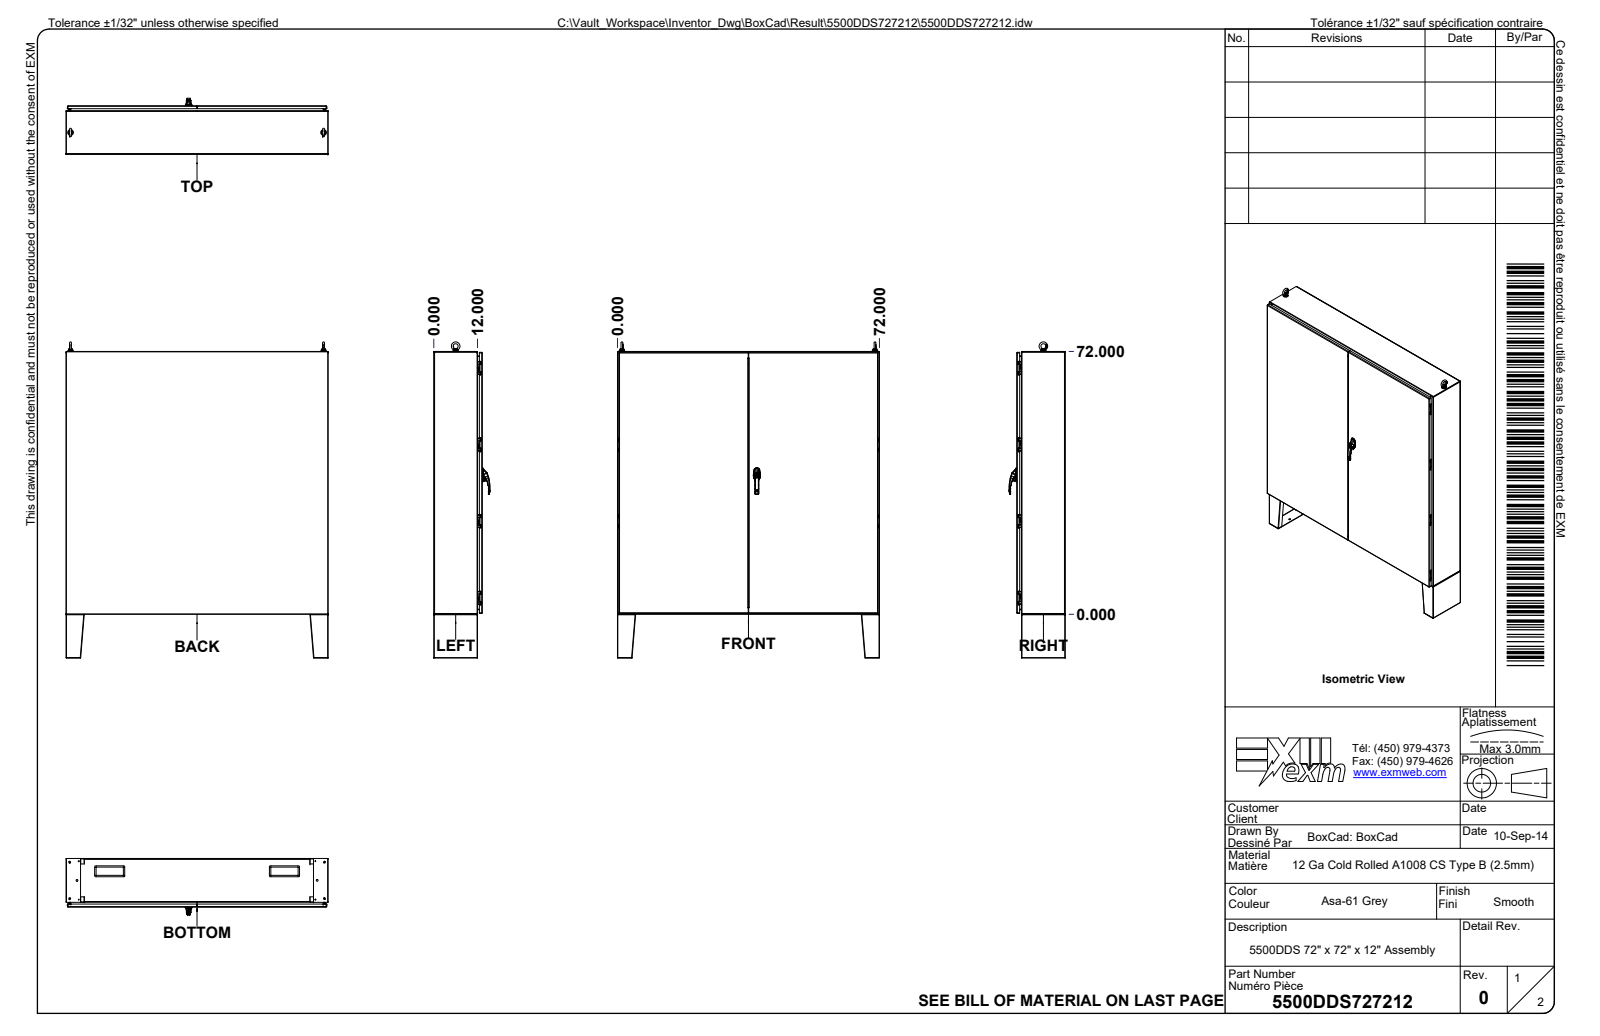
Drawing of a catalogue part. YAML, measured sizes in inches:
part_name: "5500DDS727212; 5500DDS727212B; 5500DDS727212B-P; 5500DDS727212LS-P (+8 more)"
step_written_by: "Autodesk Inventor 2024 (AUTOMOTIVE_DESIGN)"
units: inches
bodies: {solids: 275, faces: 36132, planar: 12457, cylindrical: 9061, other: 14614}
overall_size: [86.638, 72, 15.422]
volume: 2003
surface_area: 45738
round_holes:
  - {diameter: 0.177, count: 384}
  - {diameter: 0.03, count: 41}
  - {diameter: 0.201, count: 26}
  - {diameter: 0.043, count: 16}
  - {diameter: 0.167, count: 16}
  - {diameter: 0.315, count: 12}
  - {diameter: 0.394, count: 12}
  - {diameter: 0.5, count: 12}
  - {diameter: 0.512, count: 12}
  - {diameter: 0.625, count: 12}
  - {diameter: 0.203, count: 8}
  - {diameter: 0.341, count: 8}
round_bosses_or_shafts:
  - {diameter: 0.272, count: 264}
  - {diameter: 0.03, count: 41}
  - {diameter: 0.232, count: 34}
  - {diameter: 0.039, count: 30}
  - {diameter: 0.289, count: 20}
  - {diameter: 0.177, count: 20}
  - {diameter: 0.39, count: 15}
  - {diameter: 0.874, count: 8}
partial_cylinders:
  - {radius: 0.02, count: 636}
  - {radius: 0.039, count: 484}
  - {radius: 0.008, count: 285}
  - {radius: 0.012, count: 231}
  - {radius: 0.01, count: 215}
  - {radius: 0.031, count: 189}
  - {radius: 0.062, count: 166}
  - {radius: 0.01, count: 130}
face_to_face_distances: [0.089, 13.255, 0.963, 12.292, 13.166, 13.344, 0.874, 12.381, 1.052, 12.203]
hole_center_spacings: [21, 42, 1, 33.125, 74.07, 0.355, 20, 22]
